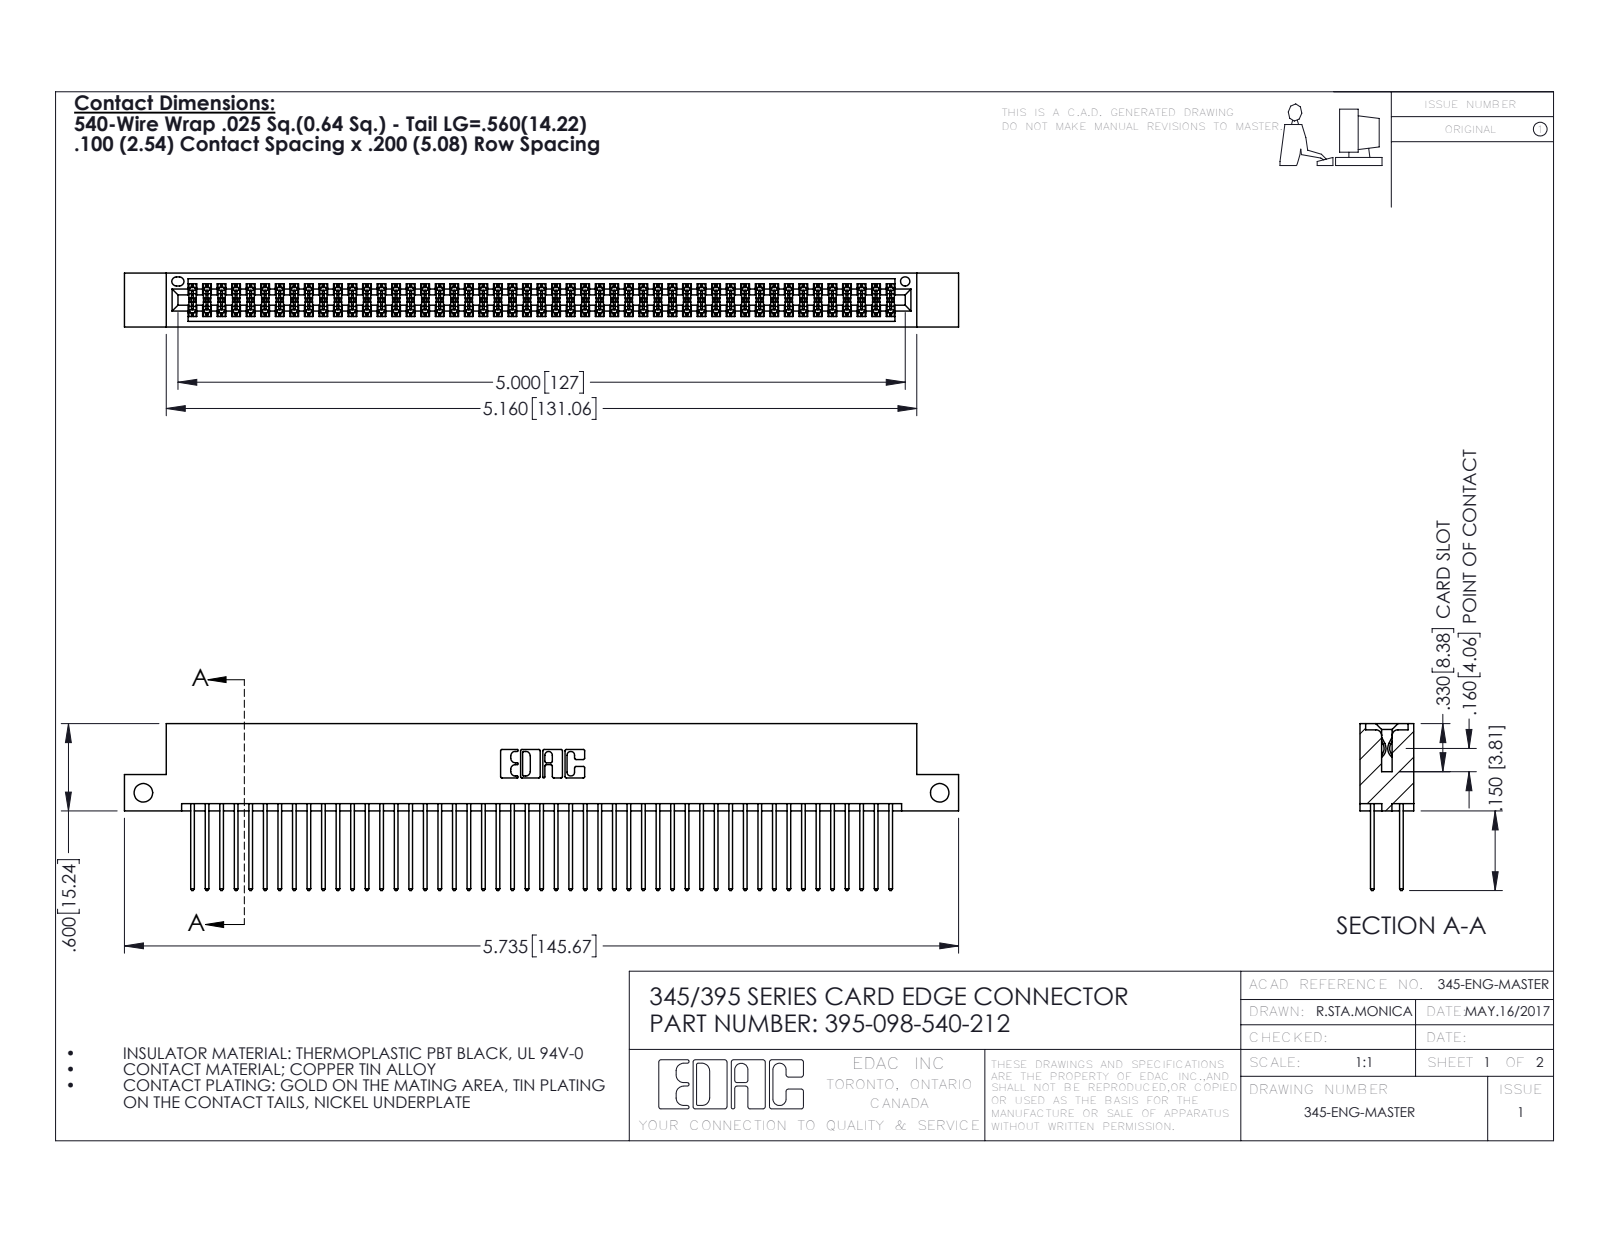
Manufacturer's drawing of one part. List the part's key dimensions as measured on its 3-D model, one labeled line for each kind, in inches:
Part name (STEP PRODUCT): 395-098-540-212; 345-292-001_345-293-140; 345 Part_Flush Mounting Lugs - Side Mount
STEP written by: SolidWorks 2016 (CONFIG_CONTROL_DESIGN)
Units: inches
Bodies: 99 solids, 5026 faces (3314 planar, 1712 cylindrical, 0 other)
Overall size (bounding box): 5.735 × 1.147 × 0.37
Volume: 0.885 in³ · Surface area: 35.89 in²
Round holes (diameter × count): ⌀0.128 ×2, ⌀0.064 ×1
Partial cylindrical surfaces — rounded edges, fillets, slot ends (radius × count): R0.006 ×147, R0.01 ×98, R0.01 ×22, R0.007 ×6, R0.031 ×6, R0.026 ×3, R0.014 ×2, R0.019 ×2
Main face-to-face distances: 0.298, 0.072, 0.2, 0.098, 0.272, 0.025, 0.37, 0.225, 0.175, 0.149
Hole centre spacings: 5.475
